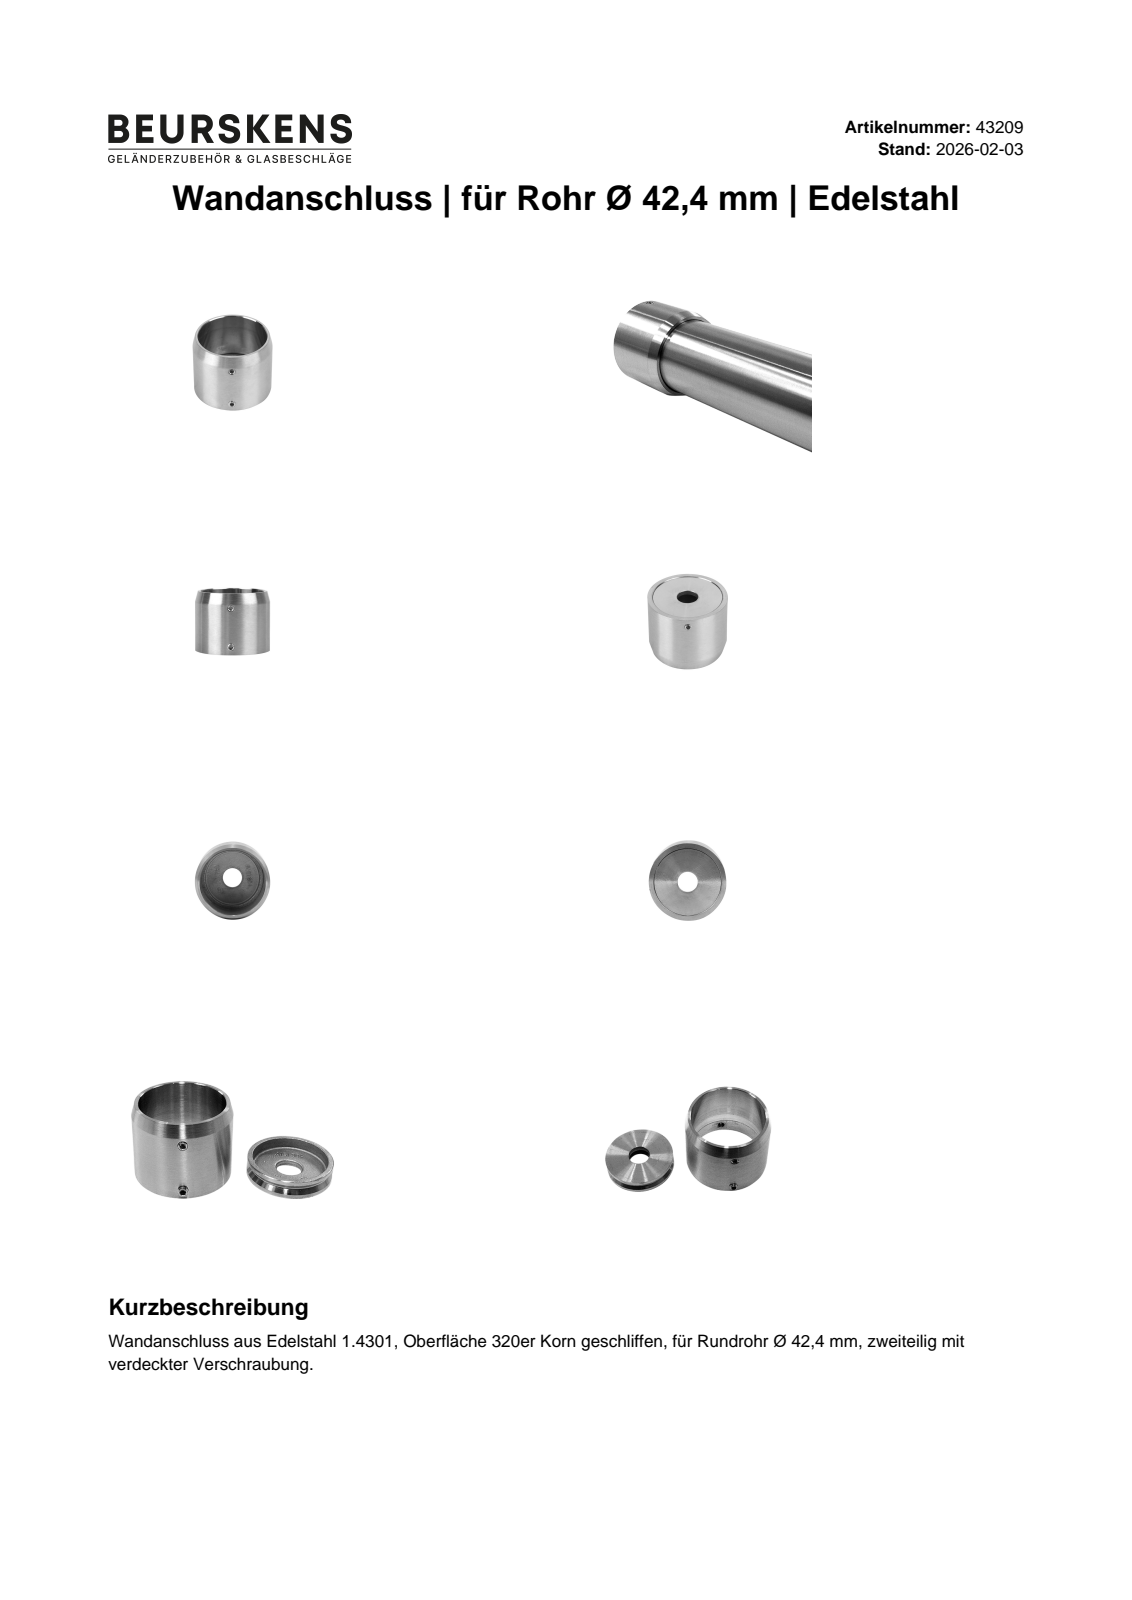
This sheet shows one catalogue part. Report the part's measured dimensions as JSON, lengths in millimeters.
{"part_name": "43209; 43209_02; DIN 913 - M5 x 5; 43209_01", "step_written_by": "Autodesk Inventor 2022 (AUTOMOTIVE_DESIGN)", "units": "millimeters", "bodies": {"solids": 5, "faces": 58, "planar": 30, "cylindrical": 13, "other": 15}, "overall_size": [50.86, 50.5, 35], "volume_mm3": 26274, "surface_area_mm2": 16367, "round_holes": [[4.8, 2], [13, 1], [37.5, 1], [42.8, 1]], "round_bosses_or_shafts": [[5, 2], [50.5, 1], [43.5, 1]], "face_to_face_distances": [4.9, 9.8, 35, 30.1, 25.2, 10.2, 5.3, 0.4, 24.8, 2.5], "hole_center_spacings": [20]}
